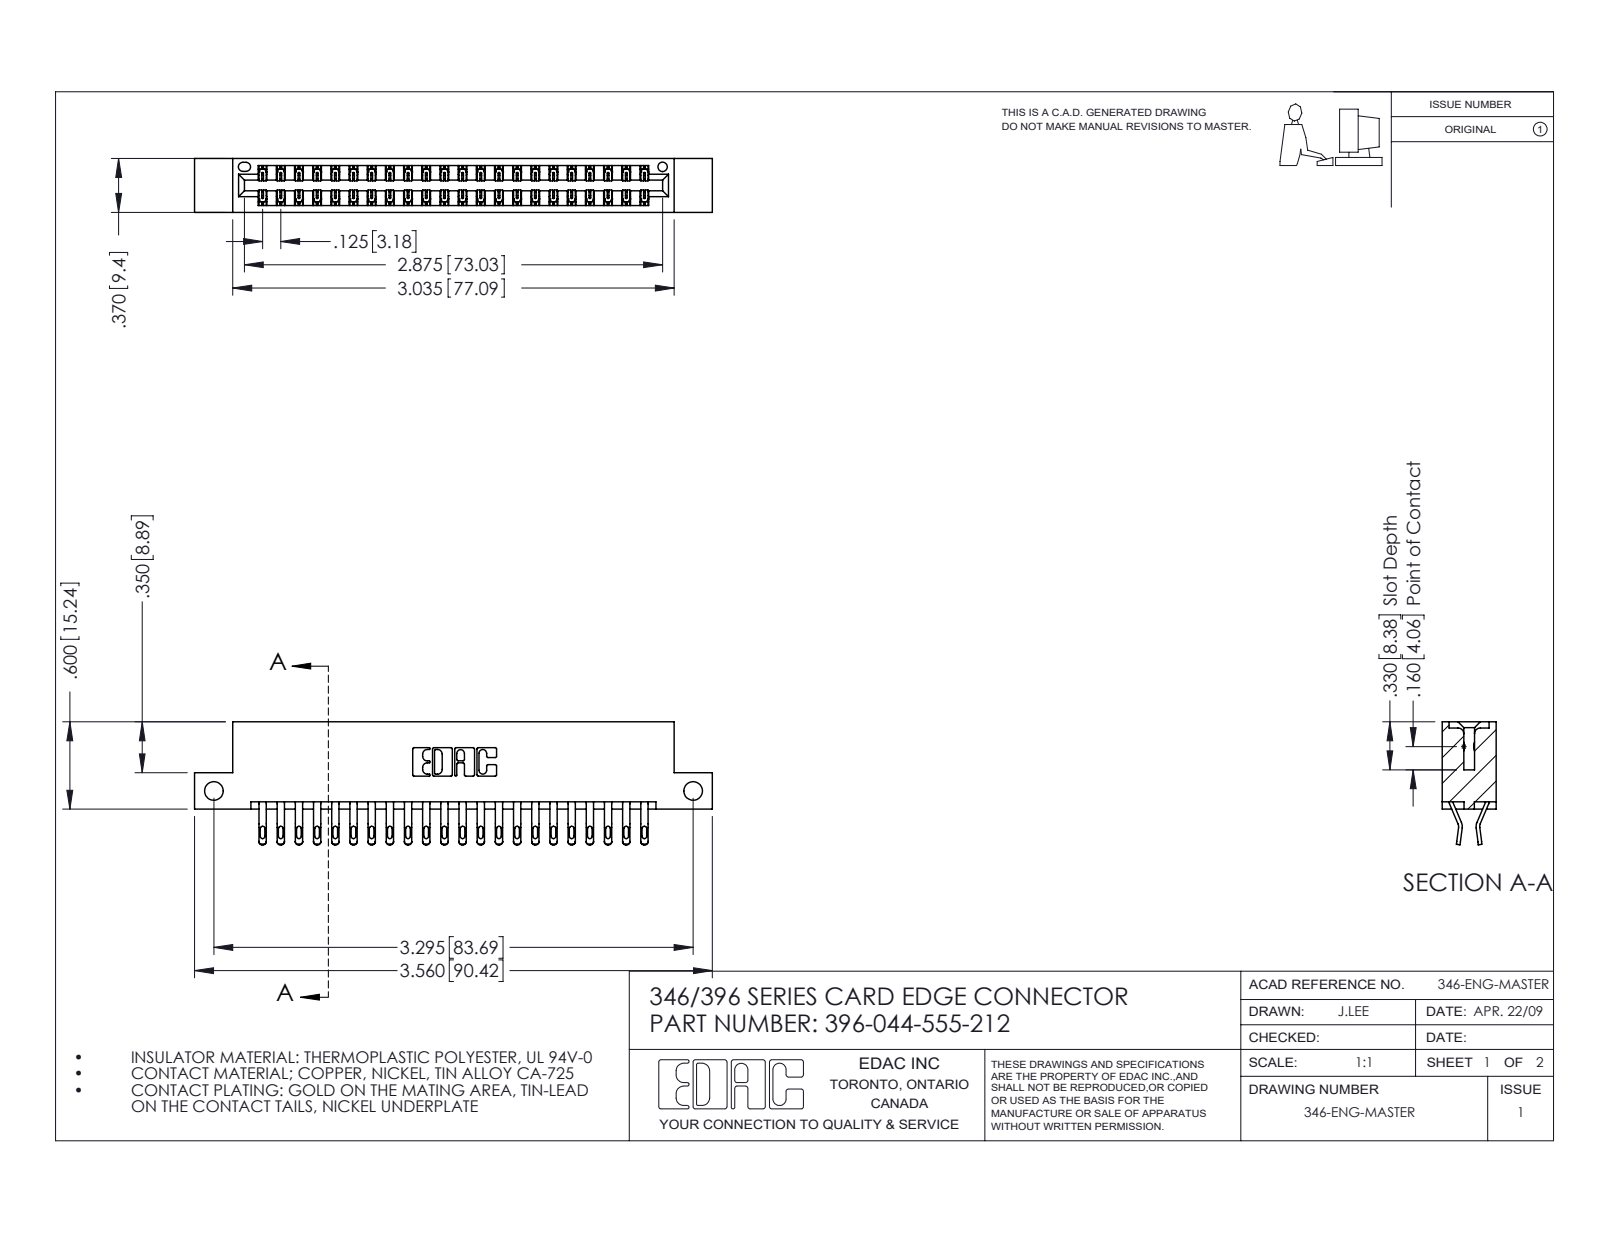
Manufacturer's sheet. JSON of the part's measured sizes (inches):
{"part_name": "345-292-001_555 Tail; 346 Part_Flush Mounting Lugs - Side Mount; 396-044-555-212", "step_written_by": "SolidWorks 2016 (CONFIG_CONTROL_DESIGN)", "units": "inches", "bodies": {"solids": 45, "faces": 2674, "planar": 1528, "cylindrical": 1146, "other": 0}, "overall_size": [3.56, 0.845, 0.37], "volume_in3": 0.531, "surface_area_in2": 18.55, "round_holes": [[0.128, 2], [0.064, 1]], "partial_cylinders_radius": [[0.016, 88], [0.02, 88], [0.006, 66], [0.01, 22], [0.007, 6], [0.031, 6], [0.026, 3], [0.01, 2]], "face_to_face_distances": [0.048, 0.322, 0.25, 0.37, 0.025, 0.072, 0.298, 0.275, 0.148, 0.222], "hole_center_spacings": [3.295]}
